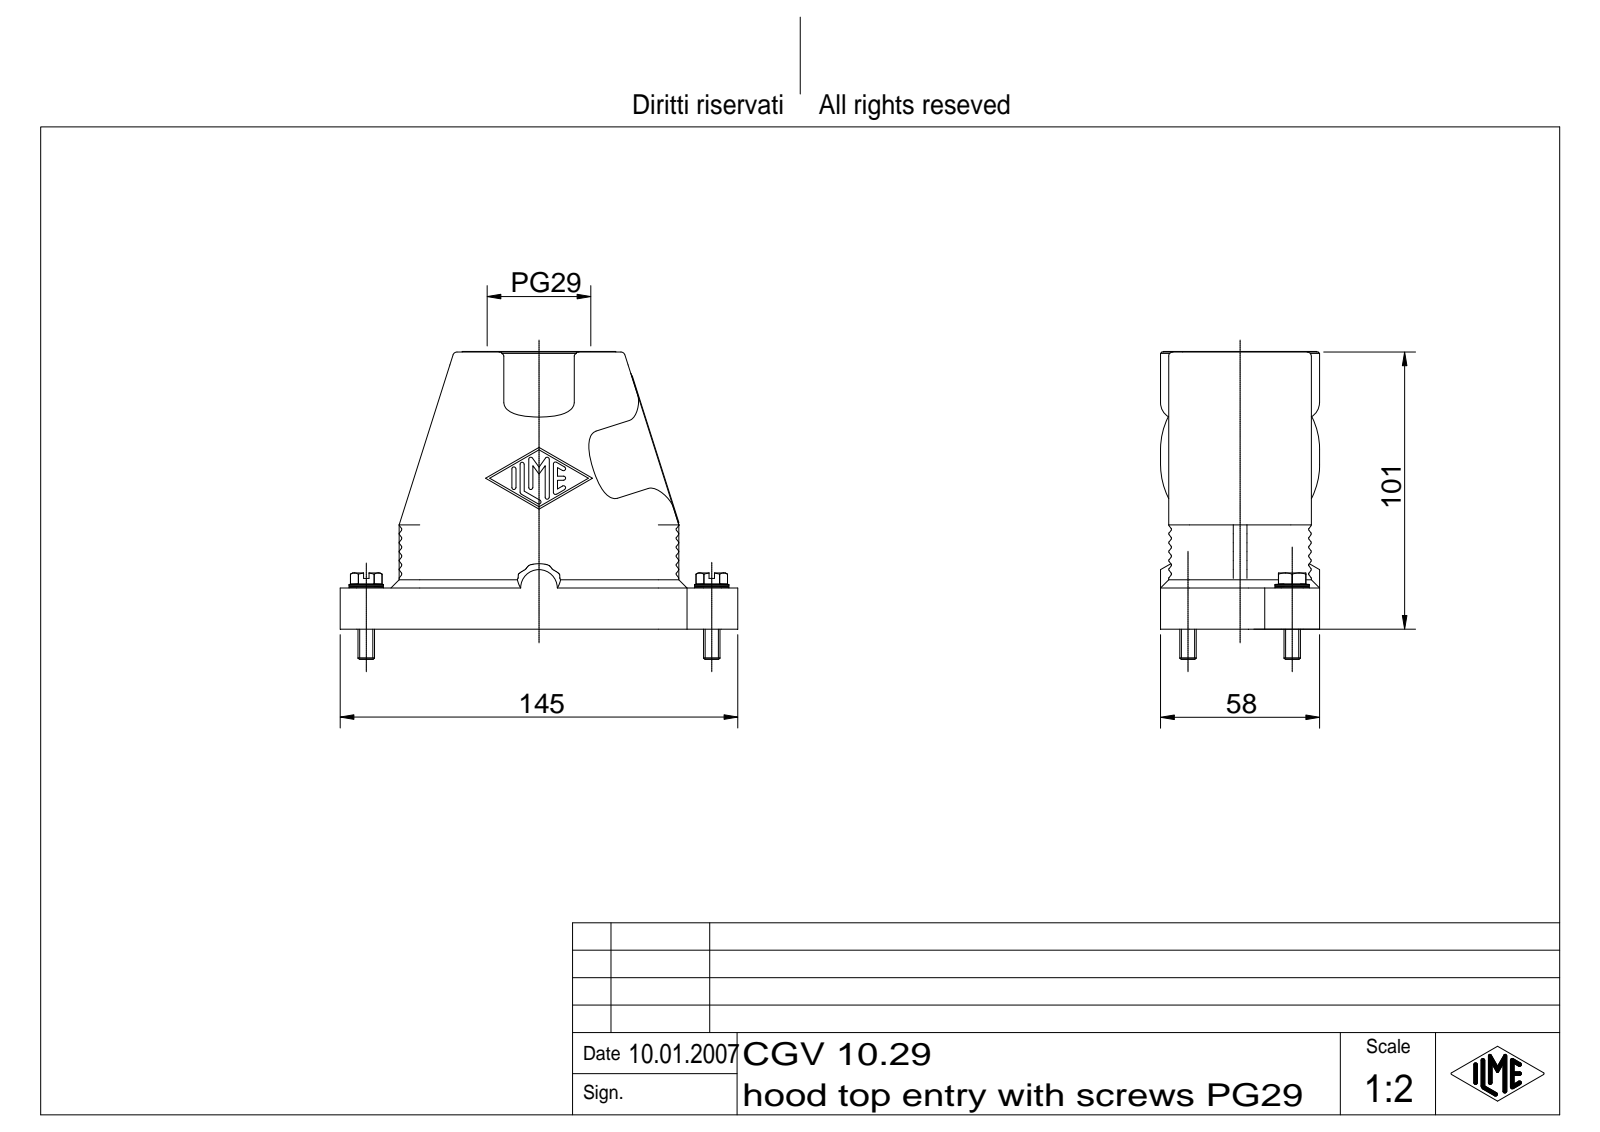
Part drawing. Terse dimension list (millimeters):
name: CGV 10.29
written by: Autodesk Inventor 7 (AUTOMOTIVE_DESIGN)
unit: mm
bodies: 3 solids, 781 faces (194 planar, 203 cylindrical, 384 other)
size: 145 × 112.2 × 58
volume: 196 470 mm³; area: 72 608 mm²
holes: 2× ⌀2.46, 2× ⌀3.2, 2× ⌀6.6, 2× ⌀15, 1× ⌀35.48
bosses: 2× ⌀56, 2× ⌀12.5, 2× ⌀6, 1× ⌀58
rounds: 39× R0.5, 14× R0.75, 8× R7.5, 6× R6, 4× R1.5, 4× R3, 2× R5.75, 2× R10.5
face distances: 3, 52, 49, 6, 55, 2.5, 46, 0.5, 58, 3.5
hole spacings: 34.94, 97.1, 63.07, 131.61
